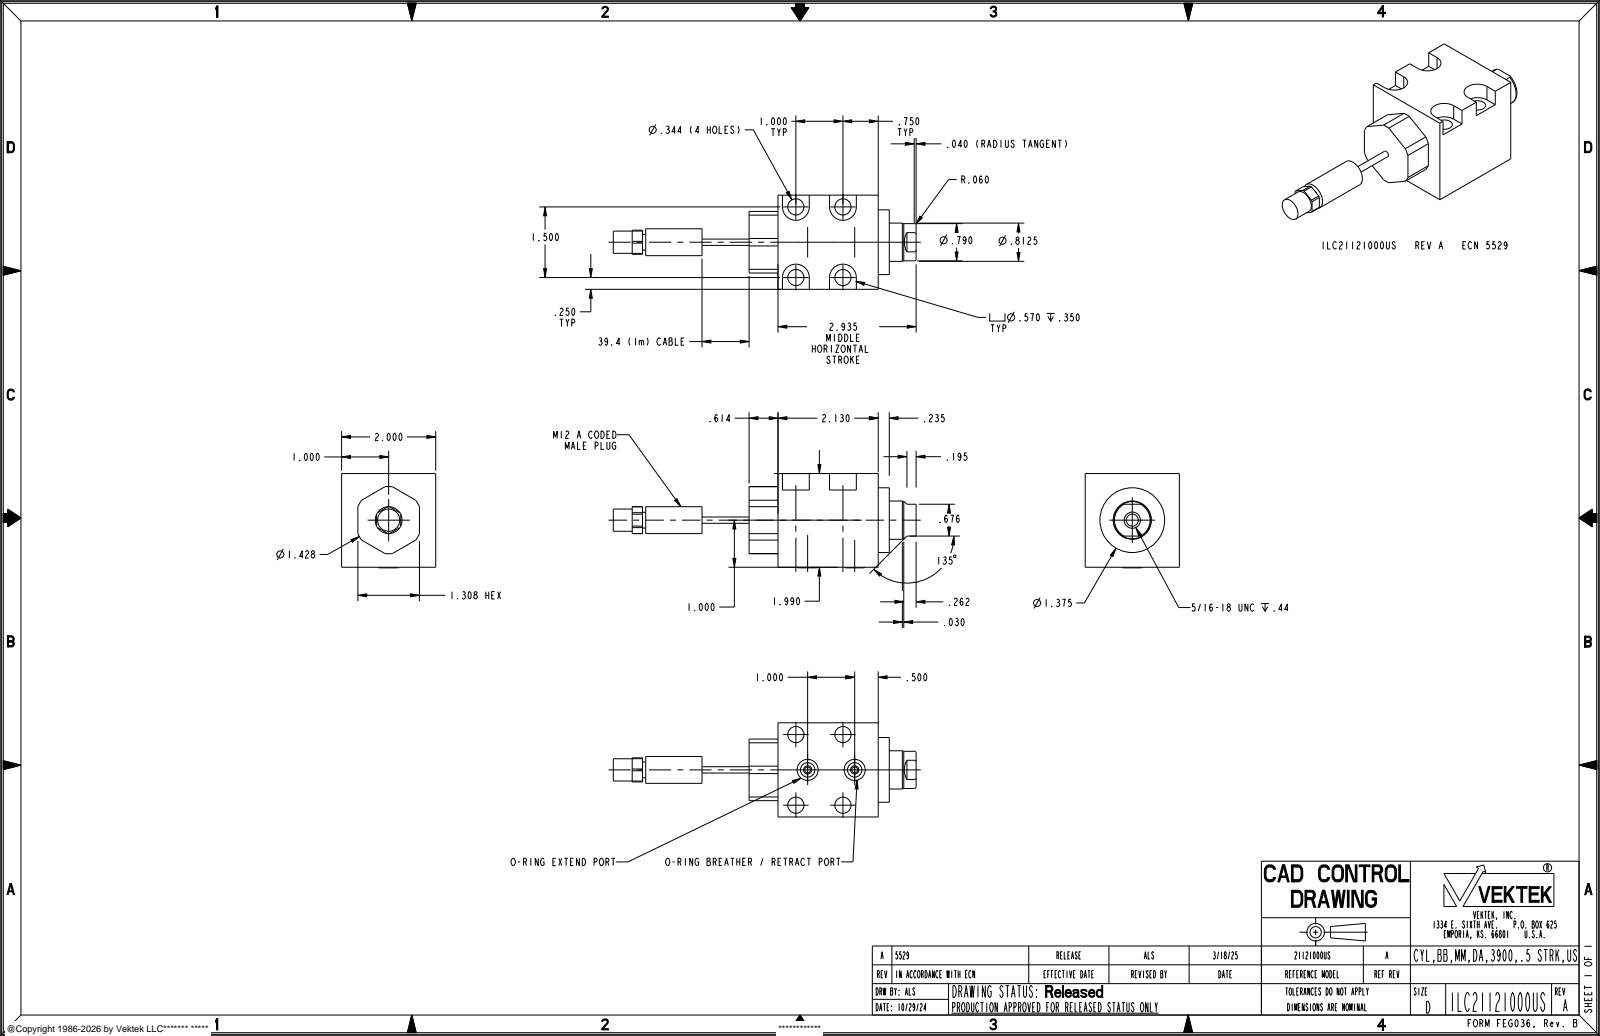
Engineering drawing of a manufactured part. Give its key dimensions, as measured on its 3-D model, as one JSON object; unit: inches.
{"part_name": "ILC21121000US", "step_written_by": "CREO PARAMETRIC BY PTC INC, 2021164 (AUTOMOTIVE_DESIGN)", "units": "inches", "bodies": {"solids": 1, "faces": 120, "planar": 46, "cylindrical": 52, "other": 22}, "overall_size": [6.435, 2.2, 2.003], "volume_in3": 9.408, "surface_area_in2": 43.86, "round_holes": [[0.344, 4], [0.125, 2], [0.447, 2], [0.257, 1]], "round_bosses_or_shafts": [[1.375, 1], [0.813, 1], [0.79, 1], [0.571, 1], [0.472, 1], [0.335, 1], [0.312, 1], [0.134, 1]], "partial_cylinders_radius": [[0.285, 4], [0.714, 1]], "face_to_face_distances": [2, 1.99, 2.13, 2.744, 0.614, 1.308, 0.235, 2.365, 2.979, 1.64], "hole_center_spacings": [0.791, 1, 1.061, 1.458, 1.5, 1.803]}
